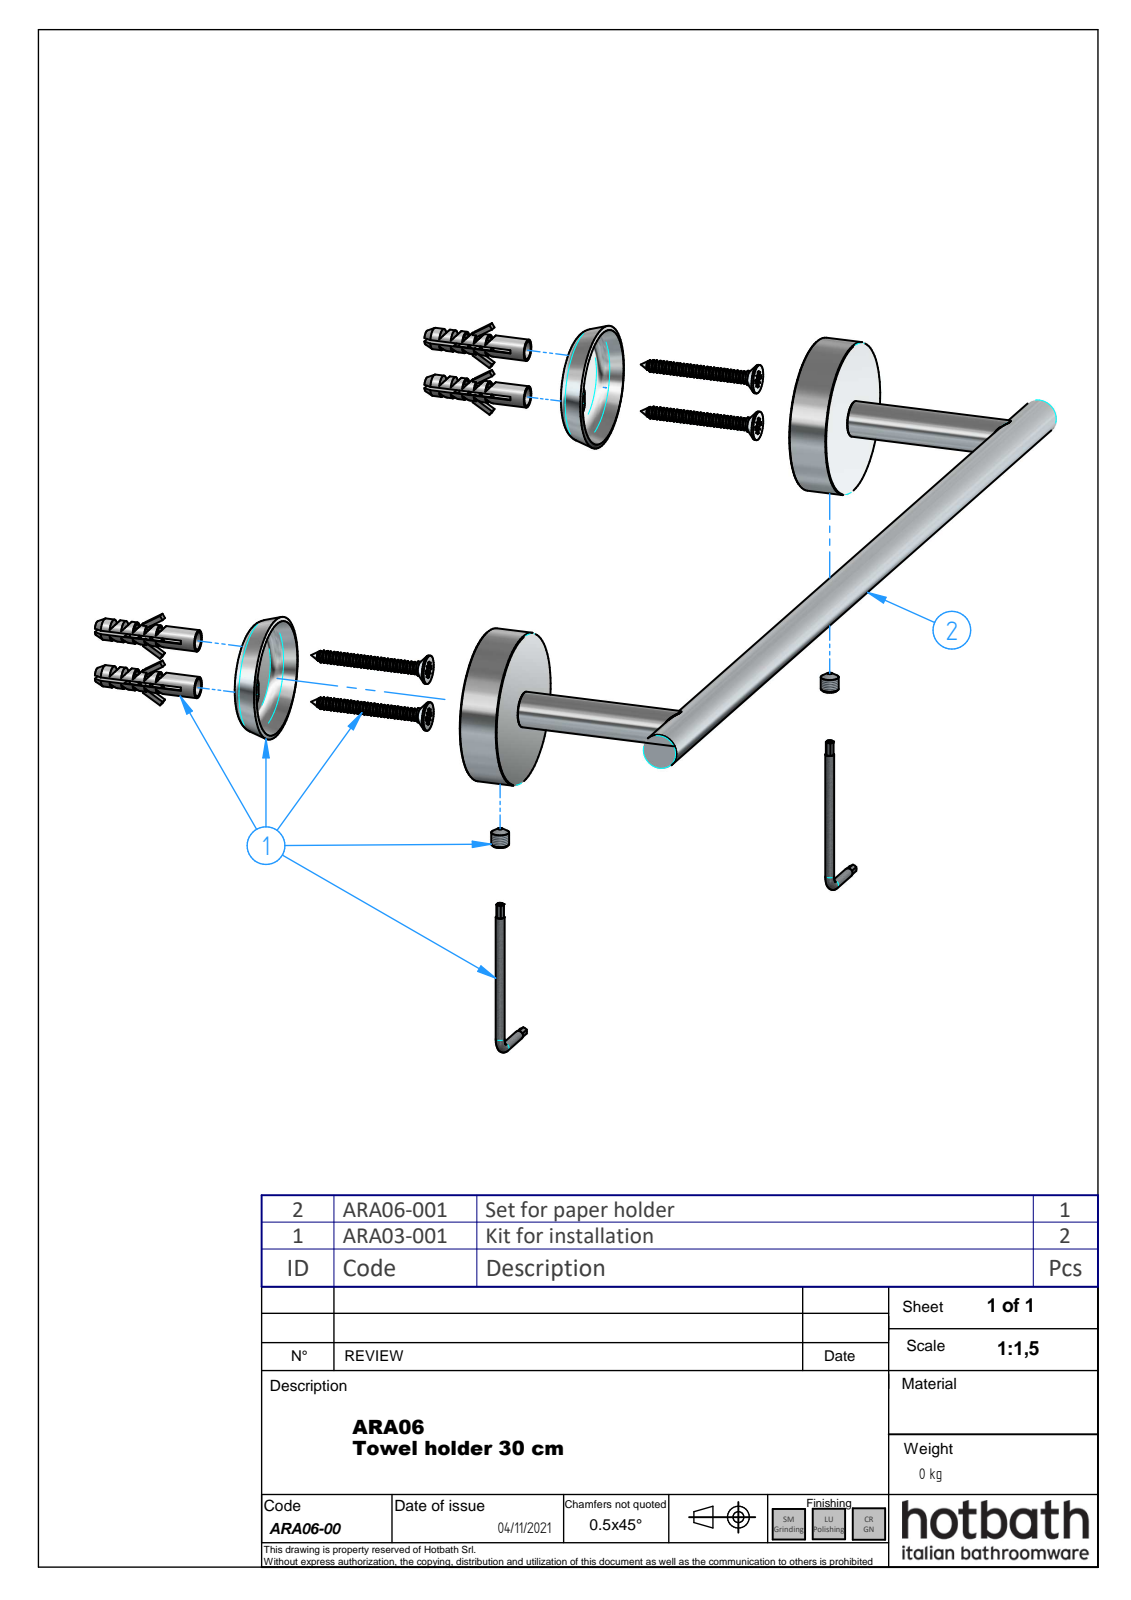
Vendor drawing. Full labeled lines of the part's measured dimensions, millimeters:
Part name (STEP PRODUCT): ARA06-00; ARA03-001_oa_0; CBA01-06; CBA01-07 (+5 more)
STEP written by: ST-DEVELOPER v16.7 (AP242_MANAGED_MODEL_BASED_3D_ENGINEERING_MIM_LF)
Units: millimetres
Bodies: 11 solids, 293 faces (224 planar, 37 cylindrical, 32 other)
Overall size (bounding box): 303 × 94 × 43
Volume: 41 007 mm³ · Surface area: 28 746 mm²
Round holes (diameter × count): ⌀4.13 ×4, ⌀5 ×4, ⌀39.4 ×2, ⌀10 ×1
Round bosses / shafts (diameter × count): ⌀6 ×4, ⌀43 ×2, ⌀10 ×2, ⌀5 ×2
Partial cylindrical surfaces — rounded edges, fillets, slot ends (radius × count): R4.35 ×2, R4.5 ×2, R17.8 ×2
Main face-to-face distances: 1.4, 11, 9.6, 1, 13.8, 2.48, 14.8, 12.8, 21, 3.43
Hole centre spacings: 260, 5.65, 8.15, 13.8, 260.06, 260.13, 260.37
